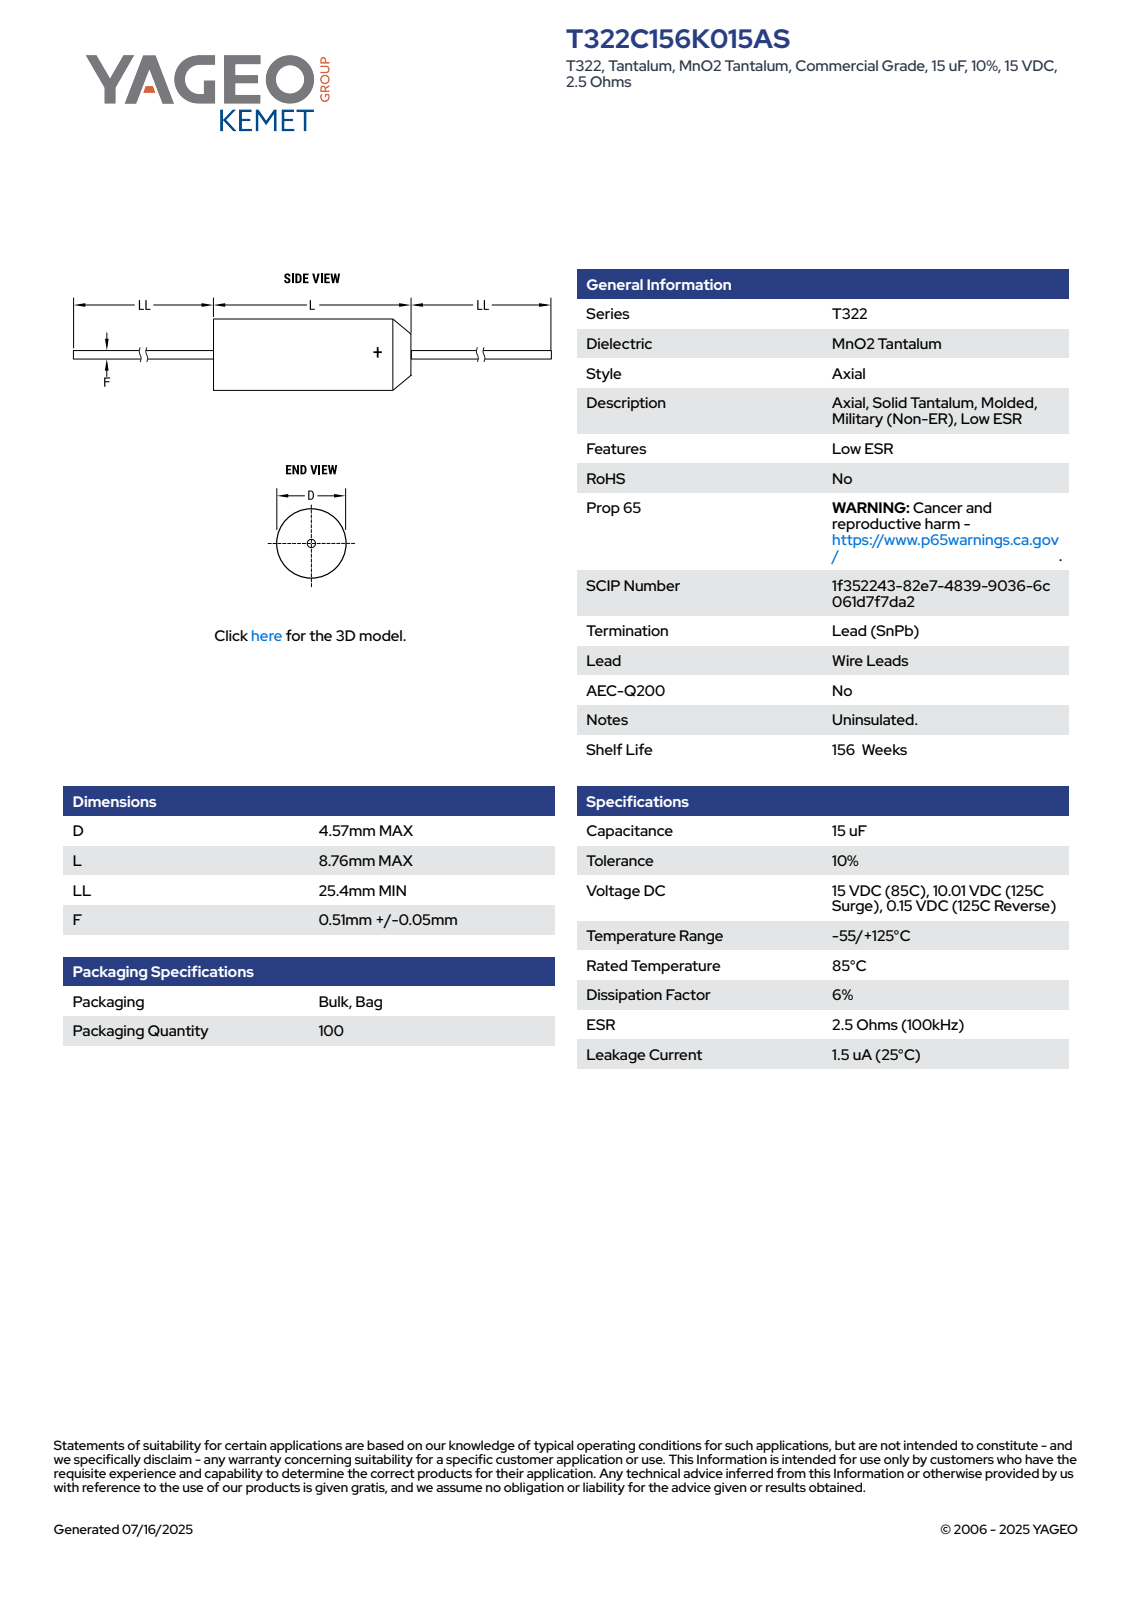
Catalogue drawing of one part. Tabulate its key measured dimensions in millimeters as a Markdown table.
| quantity | value |
| --- | --- |
| part name | CTAM_D4.57L8.76LL25.4F0.56 |
| STEP written by | SolidWorks 2020 (AUTOMOTIVE_DESIGN) |
| units | millimeters |
| bodies | 1 solid, 102 faces (38 planar, 25 cylindrical, 39 other) |
| overall size | 59.56 × 4.57 × 4.57 |
| volume | 153 mm³ |
| surface area | 241 mm² |
| round bosses / shafts (diameter × count) | 4.57 × 1, 0.56 × 1 |
| partial cylindrical surfaces (radius × count) | 2.27 × 1 |
| main face-to-face distances | 8.76, 25.4, 34.16, 59.56, 32.46, 7.06, 1.7, 27.1, 32.56, 7.16 |
